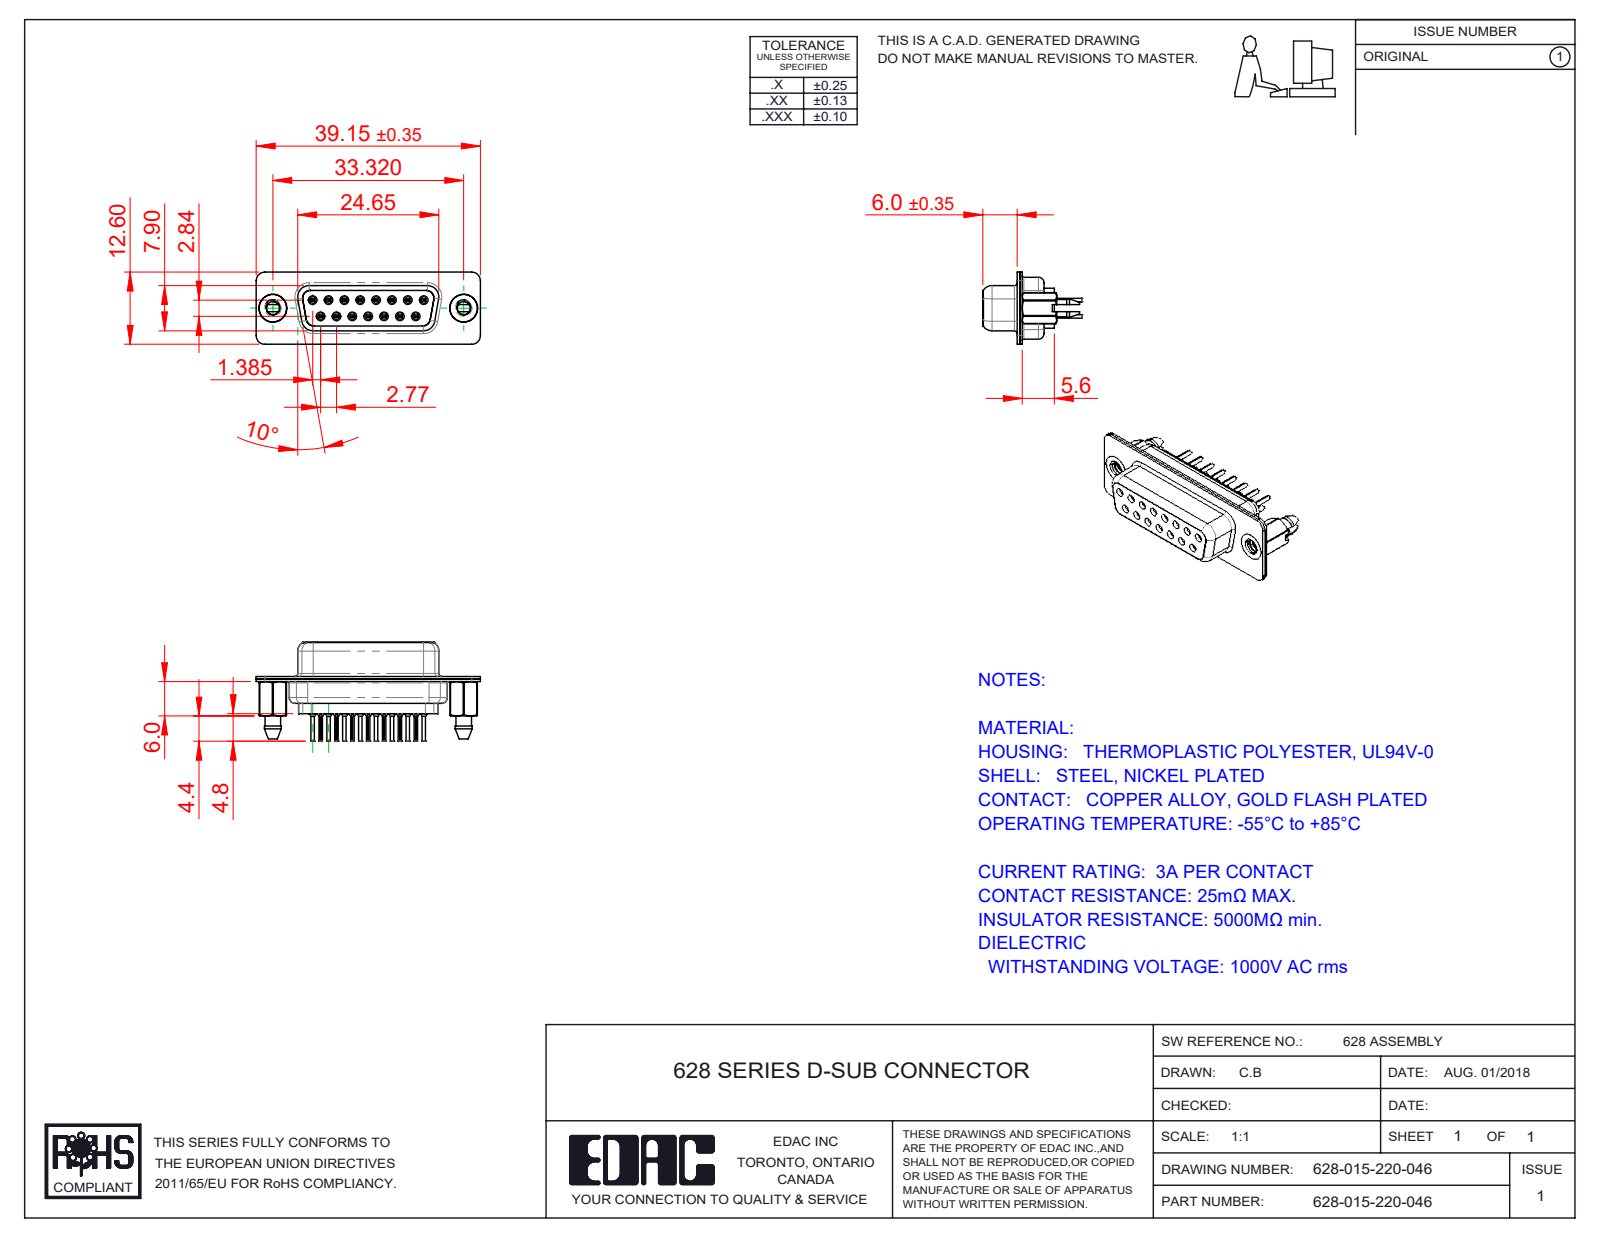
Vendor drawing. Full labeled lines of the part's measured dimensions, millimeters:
Part name (STEP PRODUCT): 628-015-220-046; 628 Contact Row 2_20L; 628 Shell Rear_15 Contacts; 628 4-40 Threaded Boardlock_LP (+3 more)
STEP written by: SolidWorks 2020 (CONFIG_CONTROL_DESIGN)
Units: millimetres
Bodies: 20 solids, 2258 faces (564 planar, 664 cylindrical, 1030 other)
Overall size (bounding box): 39.15 × 17.3 × 12.6
Volume: 2 658 mm³ · Surface area: 6 617 mm²
Round holes (diameter × count): ⌀0.2 ×15, ⌀0.8 ×15, ⌀0.9 ×15, ⌀1.1 ×15, ⌀1.6 ×15, ⌀1.7 ×8, ⌀2.26 ×2, ⌀4 ×2, ⌀4.05 ×2, ⌀4.85 ×2
Round bosses / shafts (diameter × count): ⌀2 ×15, ⌀1.5 ×15, ⌀1.2 ×15, ⌀0.6 ×15, ⌀4.95 ×2, ⌀4.8 ×2
Partial cylindrical surfaces — rounded edges, fillets, slot ends (radius × count): R0.1 ×30, R1.5 ×20, R0.28 ×15, R2 ×12, R1.35 ×8, R1.6 ×6, R0.25 ×4, R0.5 ×4
Main face-to-face distances: 0.45, 0.4, 0.9, 6.6, 1.9, 8.5, 1.4, 0.85, 7.05, 7.45
Hole centre spacings: 3.16, 2.77, 5.54, 8.31, 11.08, 5.03, 5.04, 7.48
